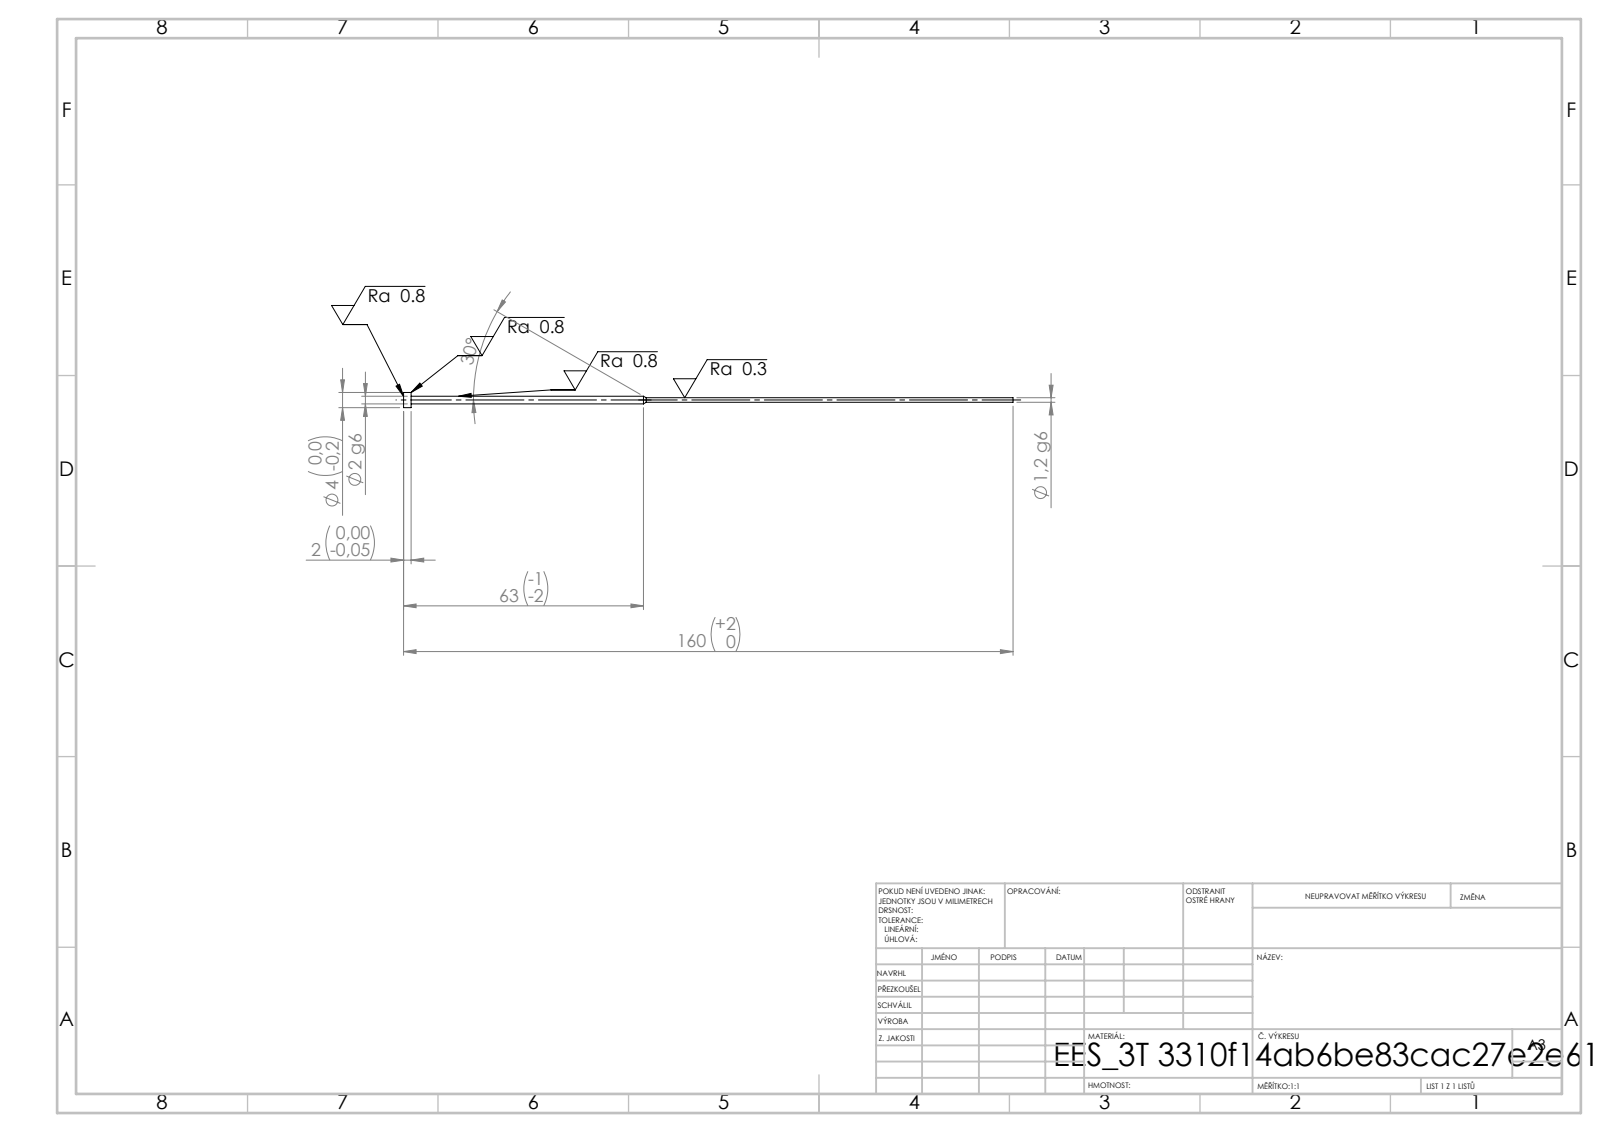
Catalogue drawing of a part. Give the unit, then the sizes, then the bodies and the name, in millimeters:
Units: millimetres
Overall size (bounding box): 160 × 4 × 4
Round bosses / shafts (diameter × count): ⌀4 ×1, ⌀2 ×1, ⌀1.2 ×1
Main face-to-face distances: 2, 158, 160
Volume: 327 mm³ · Surface area: 799 mm²
Bodies: 1 solid, 11 faces (3 planar, 6 cylindrical, 2 other)
STEP written by: SolidWorks 2019 (CONFIG_CONTROL_DESIGN)
